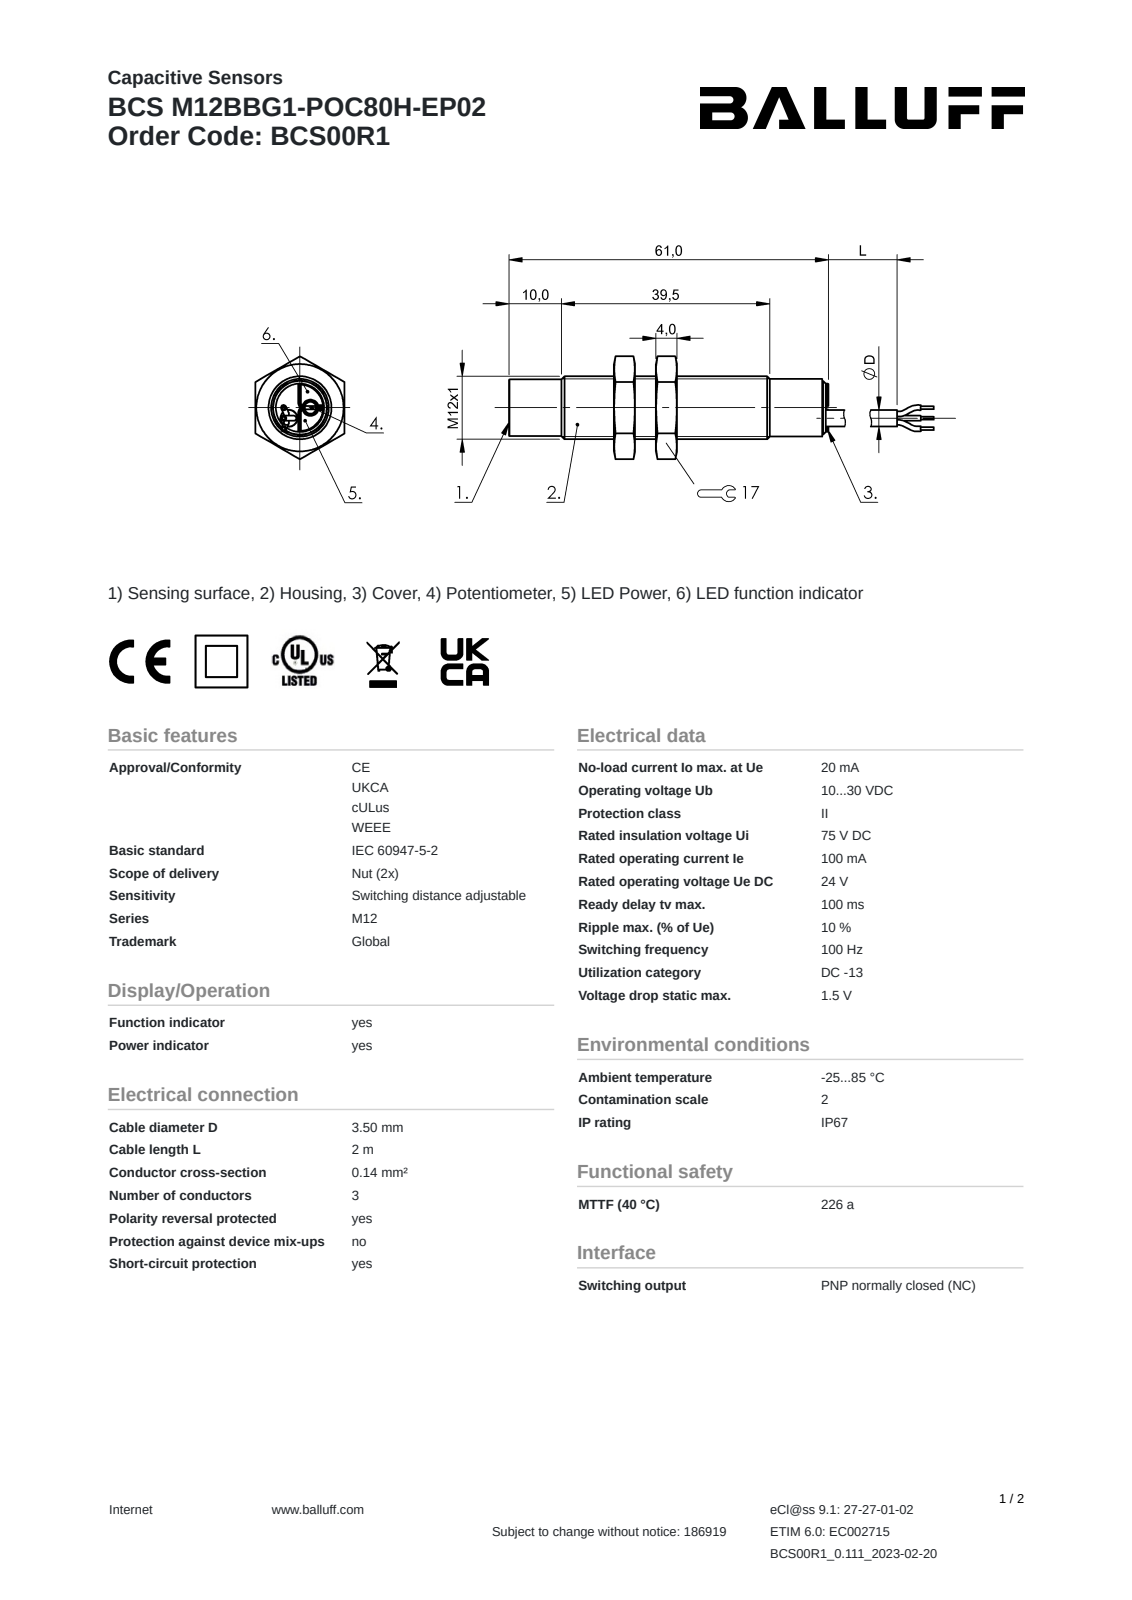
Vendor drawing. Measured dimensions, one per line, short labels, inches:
name: BCS00R1
written by: SolidWorks 2021 (AUTOMOTIVE_DESIGN)
unit: in
bodies: 3 solids, 80 faces (36 planar, 13 cylindrical, 31 other)
size: 2.764 × 0.773 × 0.669
volume: 0.457 in³; area: 5.822 in²
holes: 1× ⌀0.11, 1× ⌀0.43
bosses: 1× ⌀0.472, 1× ⌀0.413, 1× ⌀0.409, 1× ⌀0.402, 1× ⌀0.094
rounds: 1× R0.012, 1× R0.02, 1× R0.197
face distances: 0.157, 0.236, 0.669, 0.394, 0.079, 0.657, 0.815, 1.051, 0.894, 1.323
hole spacings: 0.098
